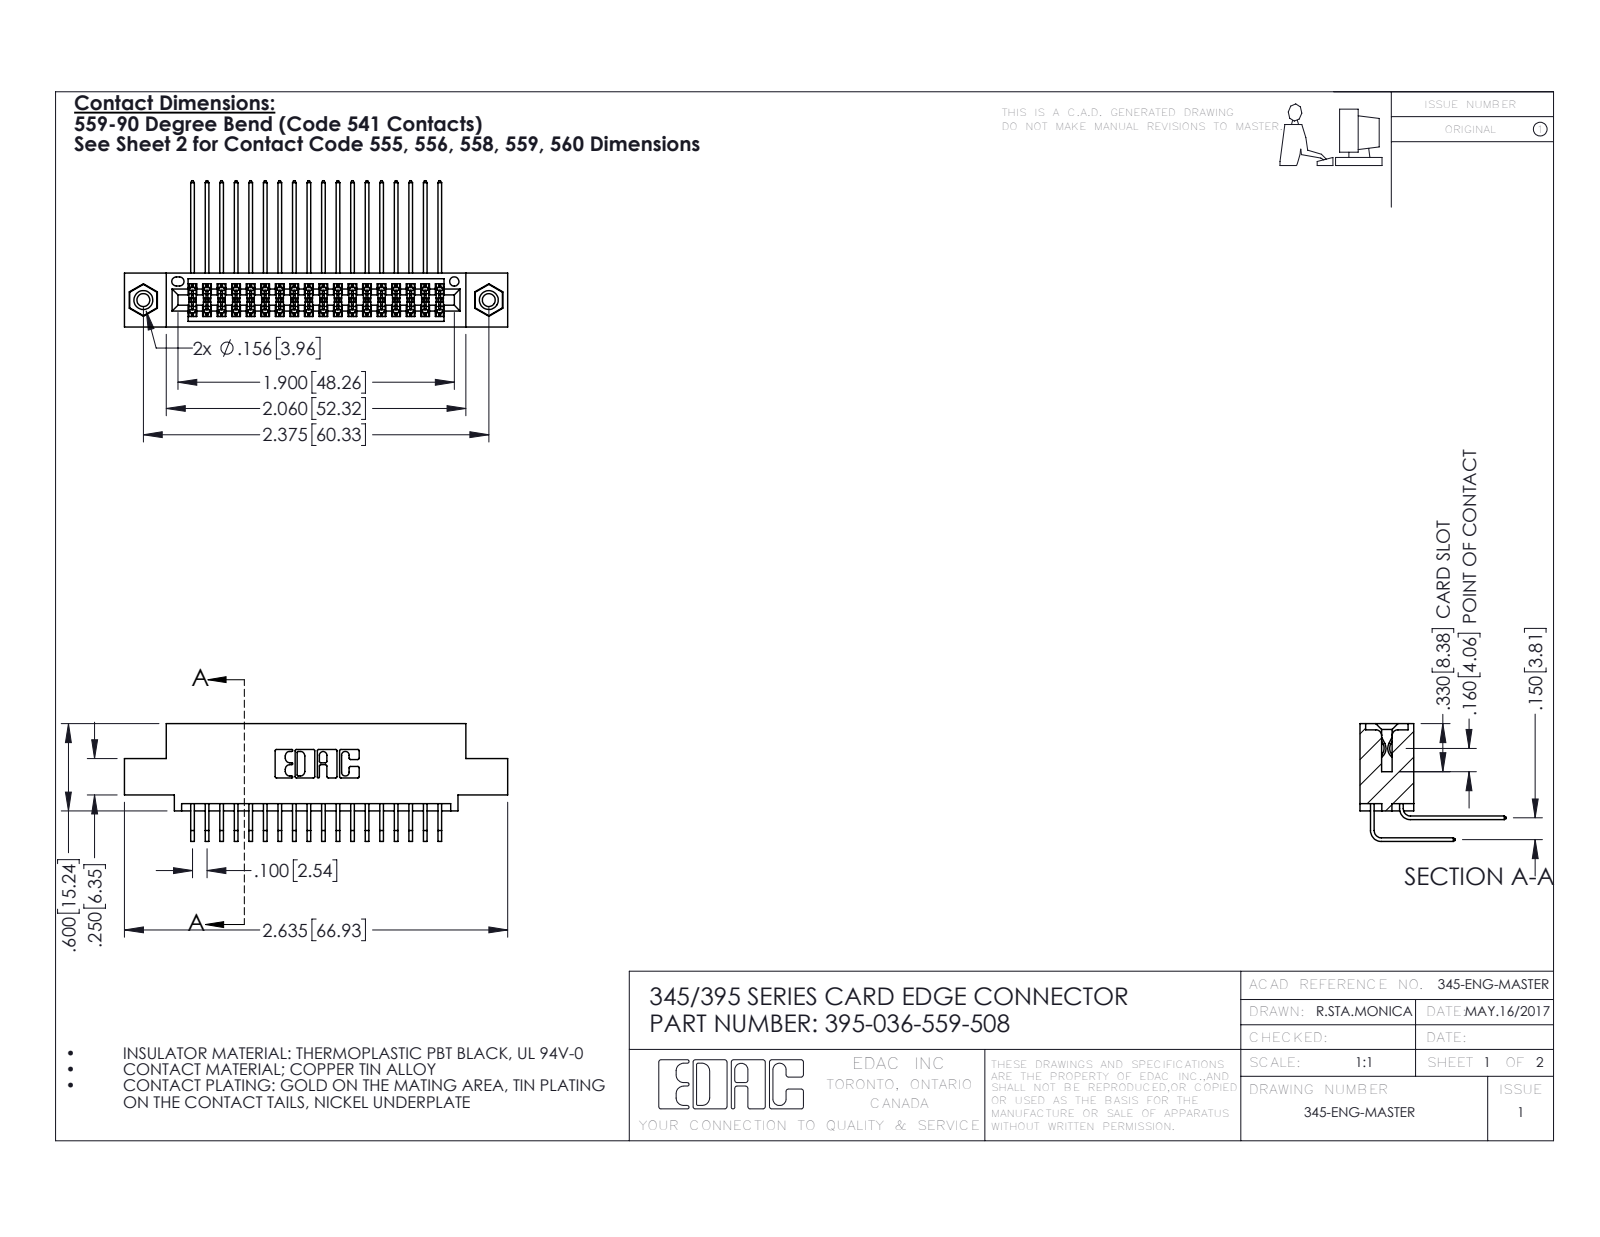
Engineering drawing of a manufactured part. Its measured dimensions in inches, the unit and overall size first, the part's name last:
Units: inches
Overall size (bounding box): 2.635 × 1.005 × 0.809
Round holes (diameter × count): ⌀0.089 ×2, ⌀0.125 ×2, ⌀0.156 ×2, ⌀0.064 ×1
Round bosses / shafts (diameter × count): ⌀0.155 ×2
Partial cylindrical surfaces — rounded edges, fillets, slot ends (radius × count): R0.006 ×54, R0.01 ×22, R0.007 ×6, R0.031 ×6, R0.026 ×3, R0.014 ×2, R0.019 ×2, R0.022 ×2
Main face-to-face distances: 0.072, 0.298, 0.2, 0.37, 0.098, 0.272, 0.025, 0.225, 0.15, 0.175
Hole centre spacings: 0.27, 2.141, 2.375
Volume: 0.391 in³ · Surface area: 15.64 in²
Bodies: 39 solids, 2062 faces (1376 planar, 670 cylindrical, 16 other)
Part name (STEP PRODUCT): 395-036-559-508; 345-292-001_558 559 Tail - 1; 345-292-001_559 Tail - 2; 345 Part_0.110 Offset - 0.156 Dia-TI (+1 more)
STEP written by: SolidWorks 2016 (CONFIG_CONTROL_DESIGN)
